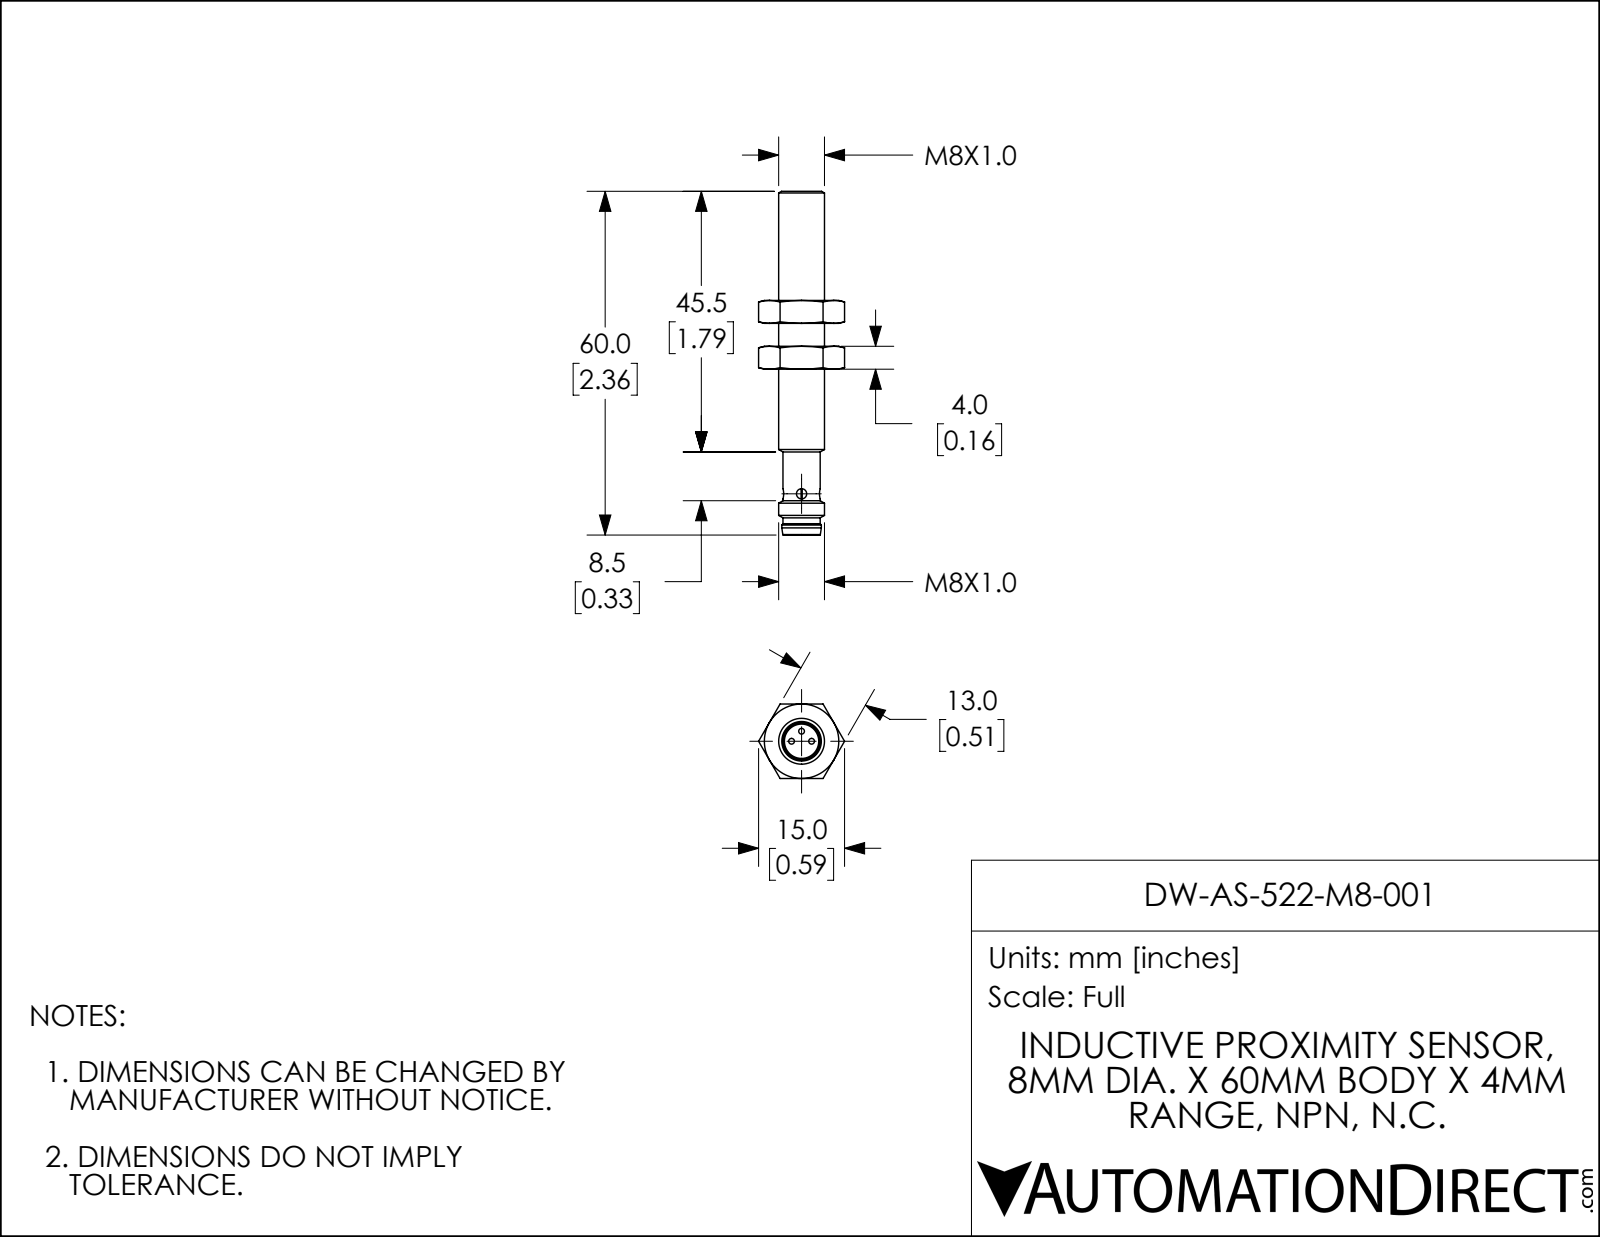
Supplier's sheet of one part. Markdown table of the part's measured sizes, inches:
| quantity | value |
| --- | --- |
| part name | DW-AS-521-M8-001 |
| STEP written by | SolidWorks 2017 (AUTOMOTIVE_DESIGN) |
| units | inches |
| bodies | 1 solid, 44 faces (13 planar, 21 cylindrical, 10 other) |
| overall size | 2.362 × 0.315 × 0.315 |
| volume | 0.163 in³ |
| surface area | 2.636 in² |
| round holes (diameter × count) | 0.071 × 2, 0.236 × 1 |
| round bosses / shafts (diameter × count) | 0.039 × 3, 0.315 × 1, 0.272 × 1, 0.256 × 1 |
| partial cylindrical surfaces (radius × count) | 0.121 × 1 |
| main face-to-face distances | 2.165, 2.362, 0.197, 0.167, 2.244, 0.079, 0.118, 1.791, 0.374, 0.453 |
